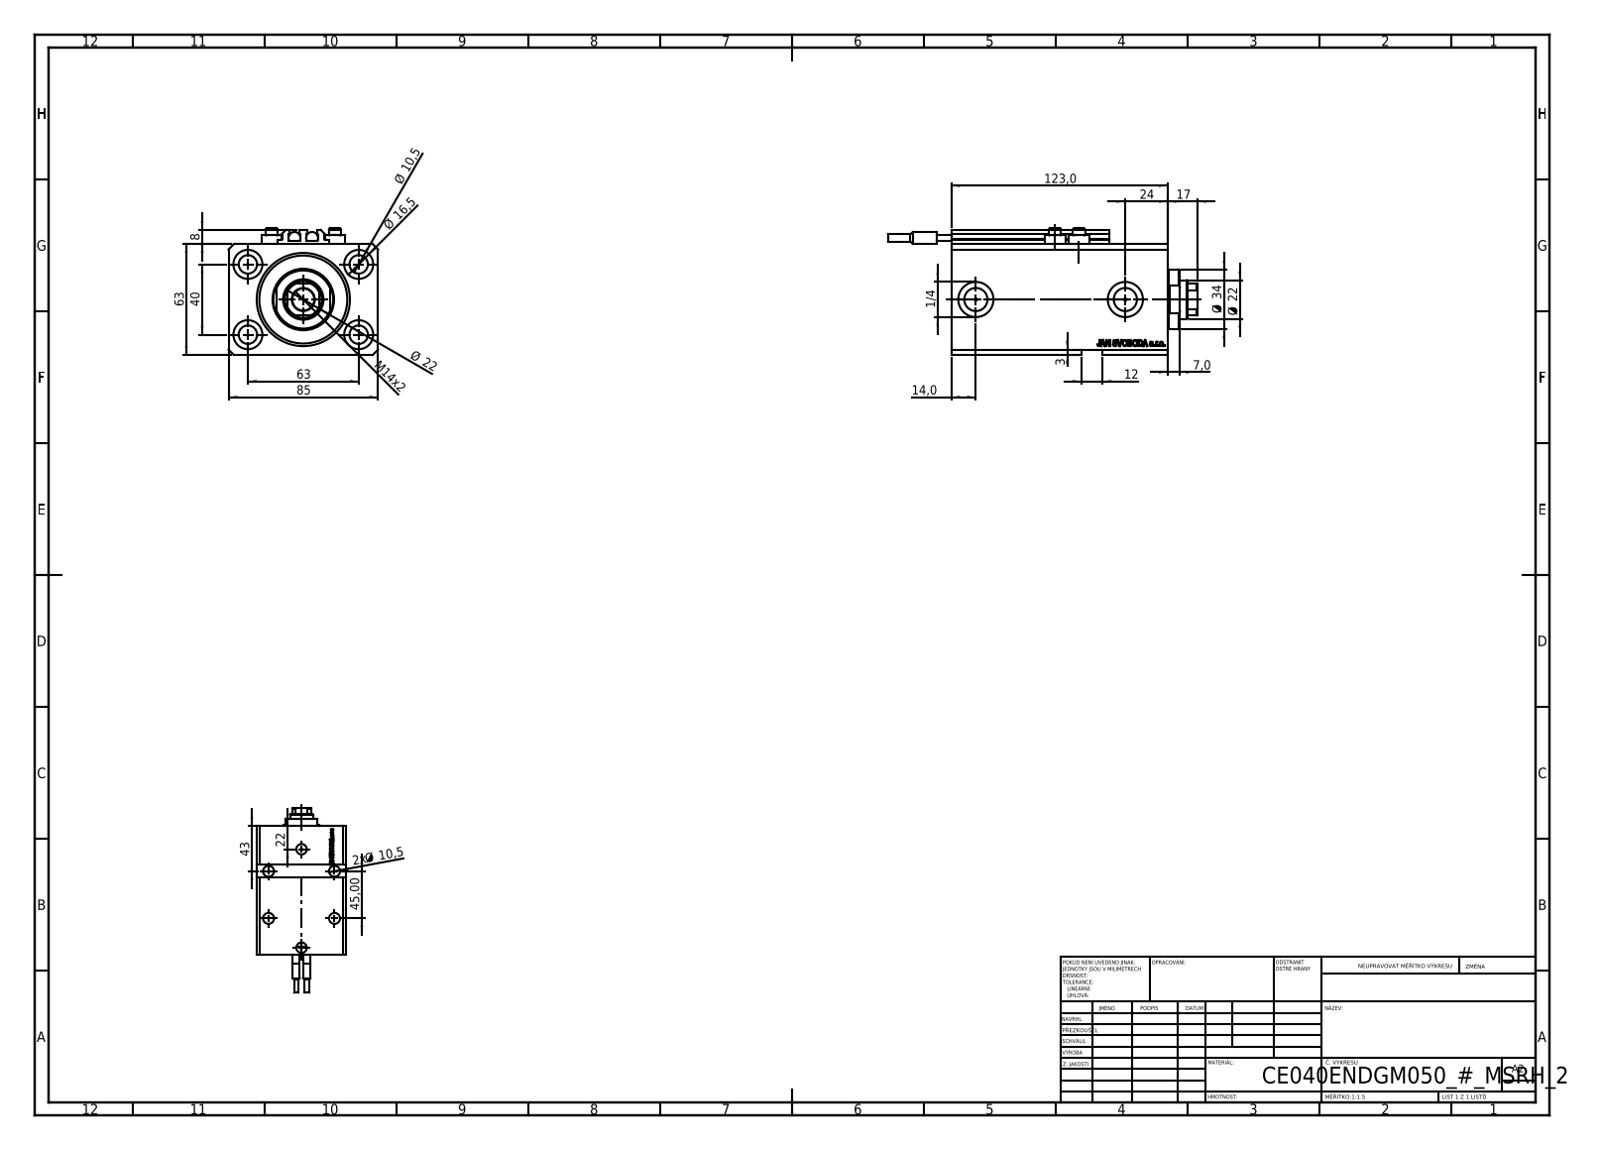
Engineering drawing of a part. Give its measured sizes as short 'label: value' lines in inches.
name: SWITCH_V250CE; V250CE_E_Body; ALLEN BOLT V250CE; V250CE_C_VCP (+1 more)
written by: SolidWorks 2019 (CONFIG_CONTROL_DESIGN)
unit: in
bodies: 10 solids, 1175 faces (571 planar, 170 cylindrical, 434 other)
size: 6.929 × 3.346 × 2.835
volume: 33.97 in³; area: 191 in²
holes: 8× ⌀0.413, 4× ⌀0.049, 4× ⌀0.157, 4× ⌀0.65, 2× ⌀0.394, 2× ⌀0.518, 2× ⌀0.787, 1× ⌀0.492, 1× ⌀0.866, 1× ⌀1.575, 1× ⌀2.087
bosses: 4× ⌀0.457, 4× ⌀0.276, 2× ⌀0.268, 2× ⌀0.256, 2× ⌀0.157, 1× ⌀1.339
rounds: 10× R0.008, 1× R0.413
face distances: 2.48, 3.346, 4.843, 0.669, 4.173, 0.118, 0.449, 3.724, 4.394, 2.559
hole spacings: 1.469, 2.48, 0.535, 0.606, 0.983, 1.084, 1.324, 1.417
